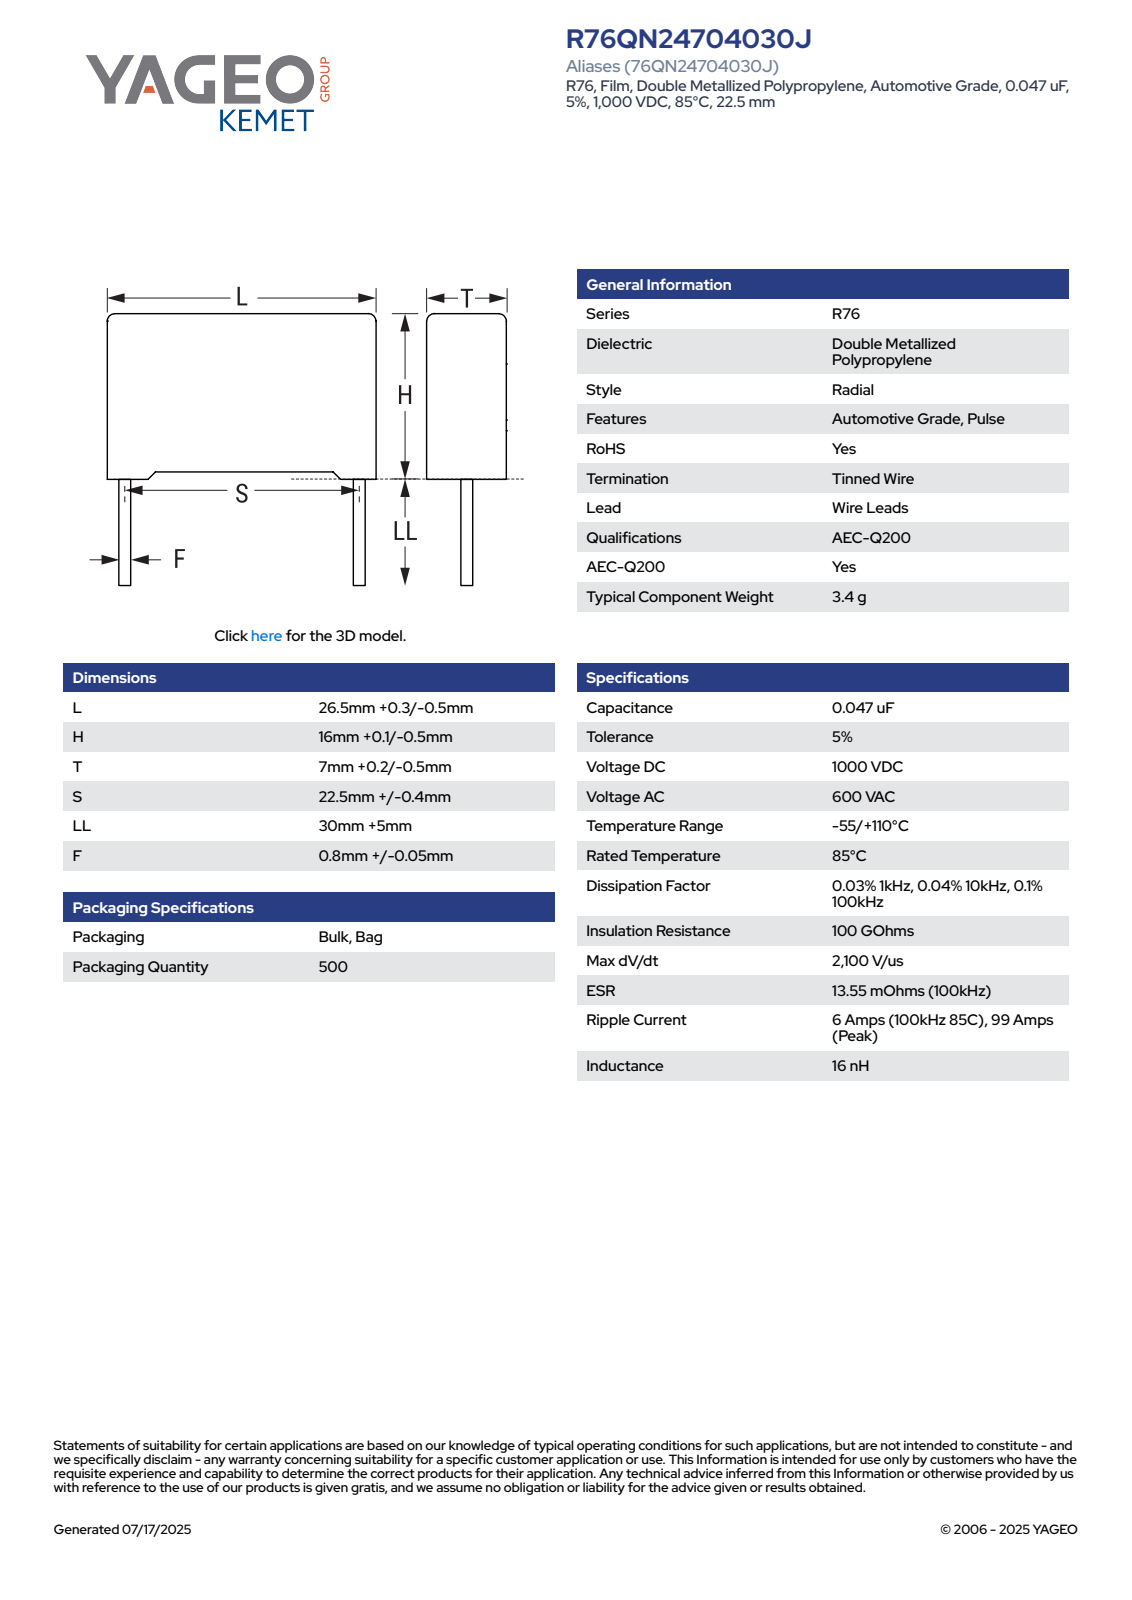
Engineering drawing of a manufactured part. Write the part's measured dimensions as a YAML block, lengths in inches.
part_name: "CFR_RB2_26.5X16X7_L26.8H16.1T7.2S22.5LL35F0.85"
step_written_by: "SolidWorks 2021 (AUTOMOTIVE_DESIGN)"
units: inches
bodies: {solids: 4, faces: 85, planar: 77, cylindrical: 8, other: 0}
overall_size: [2.012, 1.055, 0.284]
volume: 0.185
surface_area: 2.658
round_bosses_or_shafts:
  - {diameter: 0.033, count: 2}
partial_cylinders:
  - {radius: 0.02, count: 4}
face_to_face_distances: [0.283, 0.604, 1.055, 0.612, 0.035, 0.022, 0.03, 0.634, 0.248, 0.213]
